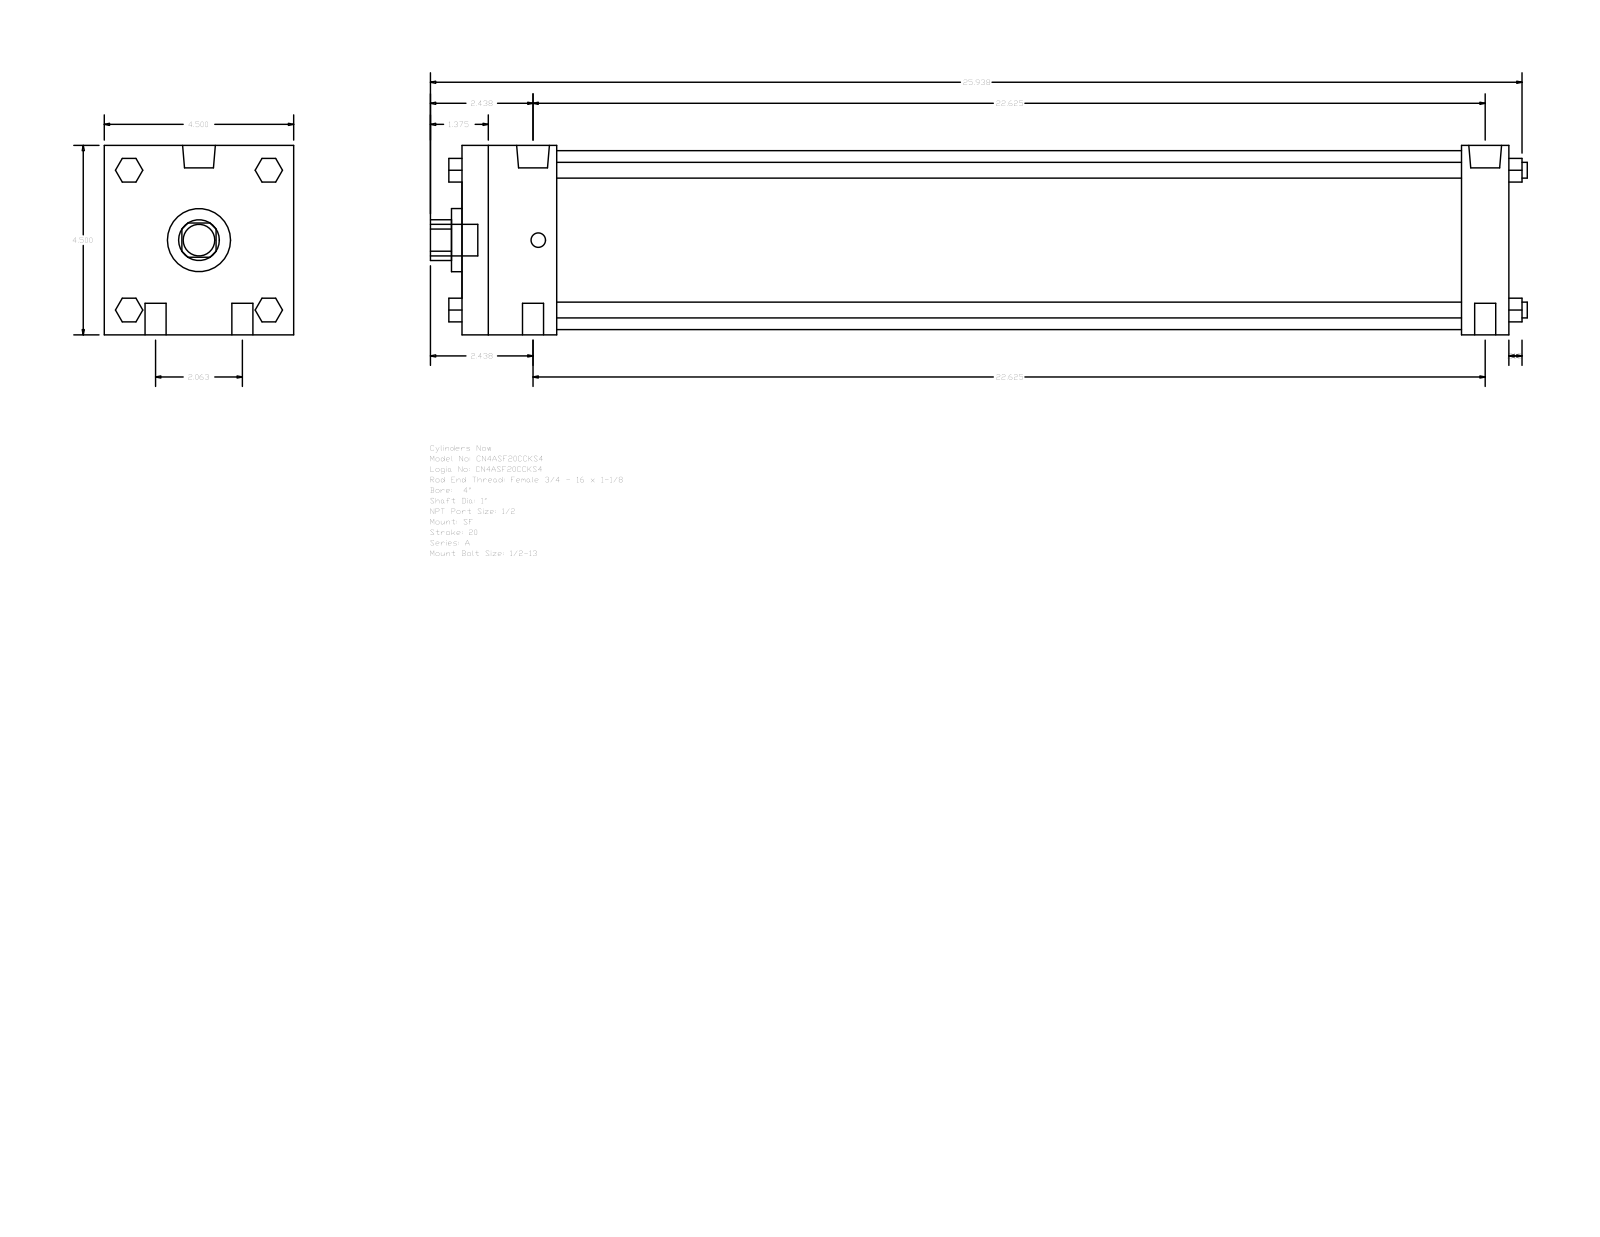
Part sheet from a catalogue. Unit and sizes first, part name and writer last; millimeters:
Units: millimetres
Overall size (bounding box): 661.99 × 114.3 × 114.3
Round holes (diameter × count): ⌀25.4 ×1, ⌀38.1 ×1, ⌀107.95 ×1
Round bosses / shafts (diameter × count): ⌀12.7 ×4, ⌀9.53 ×4, ⌀19.77 ×2, ⌀8.73 ×2, ⌀19.05 ×1
Partial cylindrical surfaces — rounded edges, fillets, slot ends (radius × count): R12.29 ×1
Main face-to-face distances: 114.3, 631.83, 603.25, 28.58, 57.15, 546.1, 574.68, 14.29, 42.16, 73.03
Bodies: 0 solids, 124 faces (94 planar, 30 cylindrical, 0 other)
Part name (STEP PRODUCT): A_SF__0400_1
STEP written by: GSSL Pune (CONFIG_CONTROL_DESIGN)
